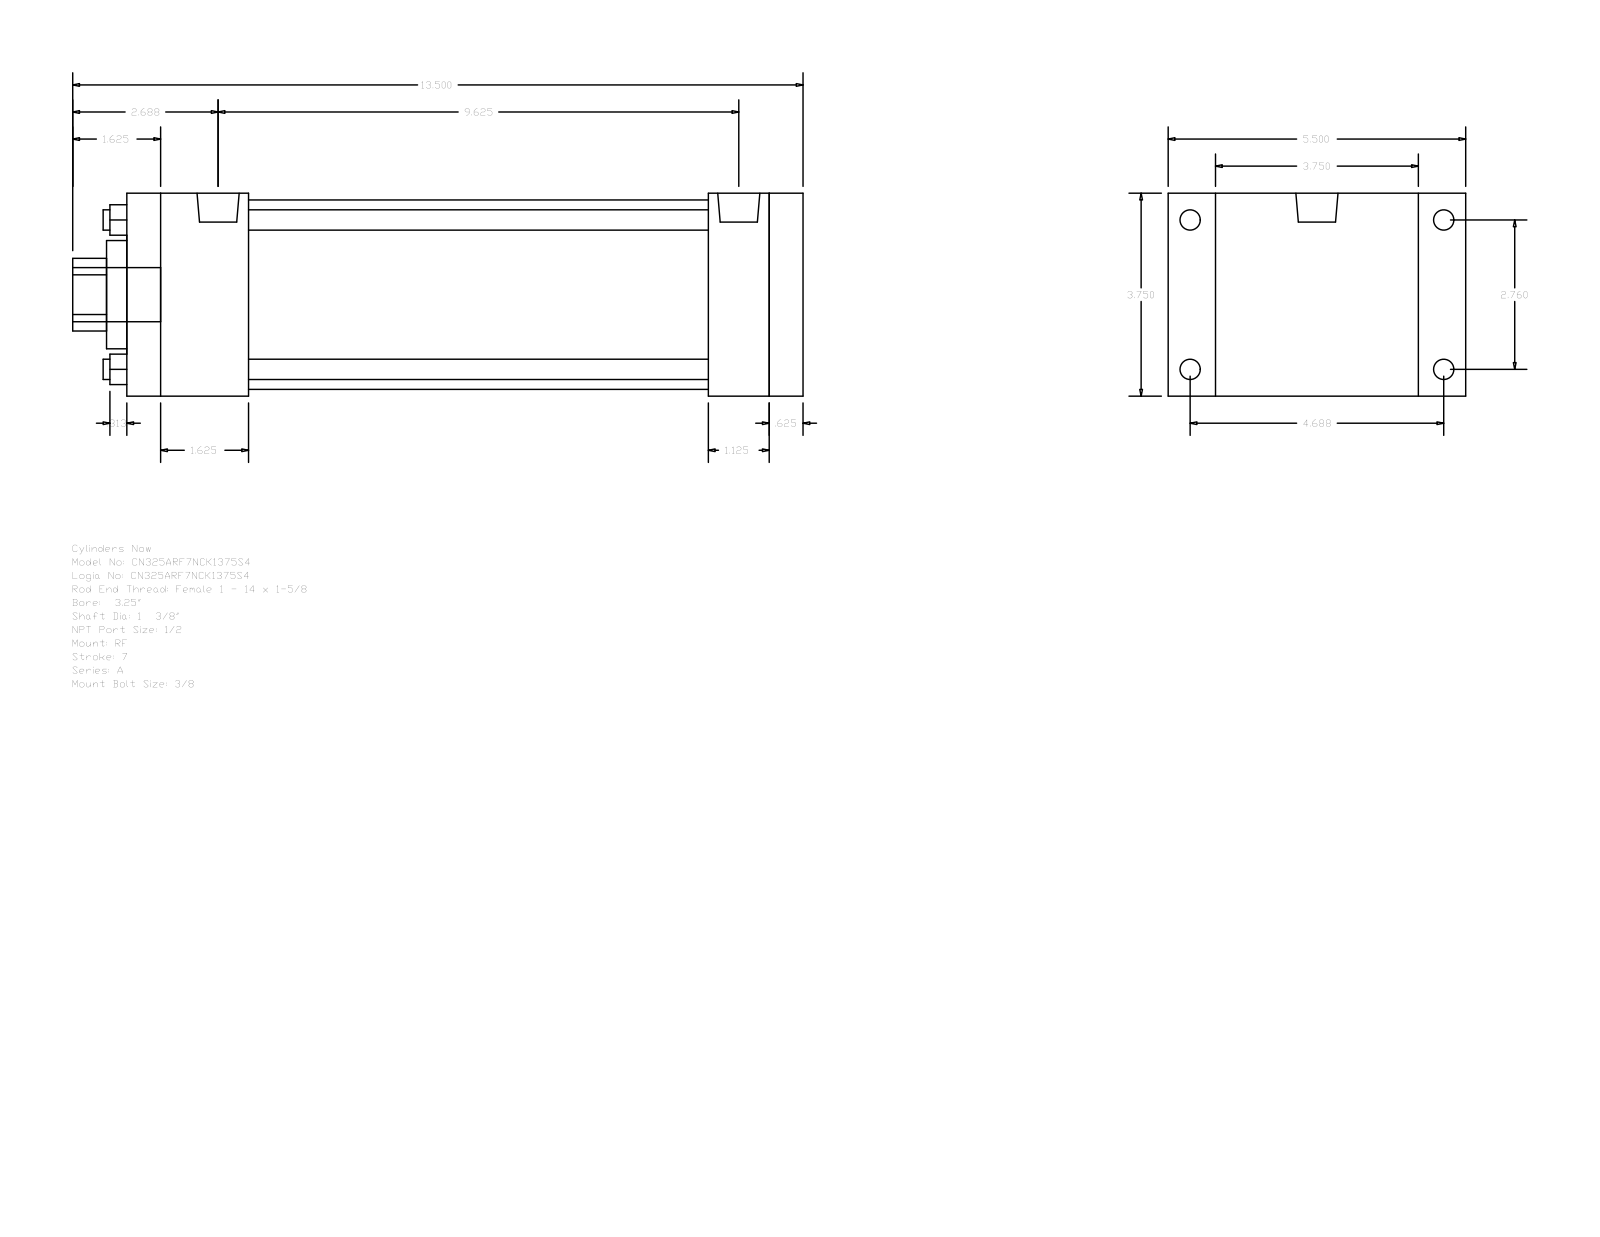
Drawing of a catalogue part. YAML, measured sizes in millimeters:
part_name: "A_RF__0325_1.375"
step_written_by: "GSSL Pune (CONFIG_CONTROL_DESIGN)"
units: millimeters
bodies: {solids: 0, faces: 92, planar: 64, cylindrical: 28, other: 0}
overall_size: [342.9, 139.7, 95.25]
round_holes:
  - {diameter: 9.53, count: 4}
  - {diameter: 34.92, count: 1}
  - {diameter: 50.8, count: 1}
  - {diameter: 88.9, count: 1}
round_bosses_or_shafts:
  - {diameter: 9.53, count: 4}
  - {diameter: 8.73, count: 4}
  - {diameter: 19.77, count: 2}
  - {diameter: 25.4, count: 1}
partial_cylinders:
  - {radius: 17.06, count: 1}
face_to_face_distances: [95.24, 317.5, 15.88, 301.62, 22.23, 117.47, 28.57, 273.05, 44.45, 57.15]
hole_center_spacings: [49.57, 70.1, 99.14]
